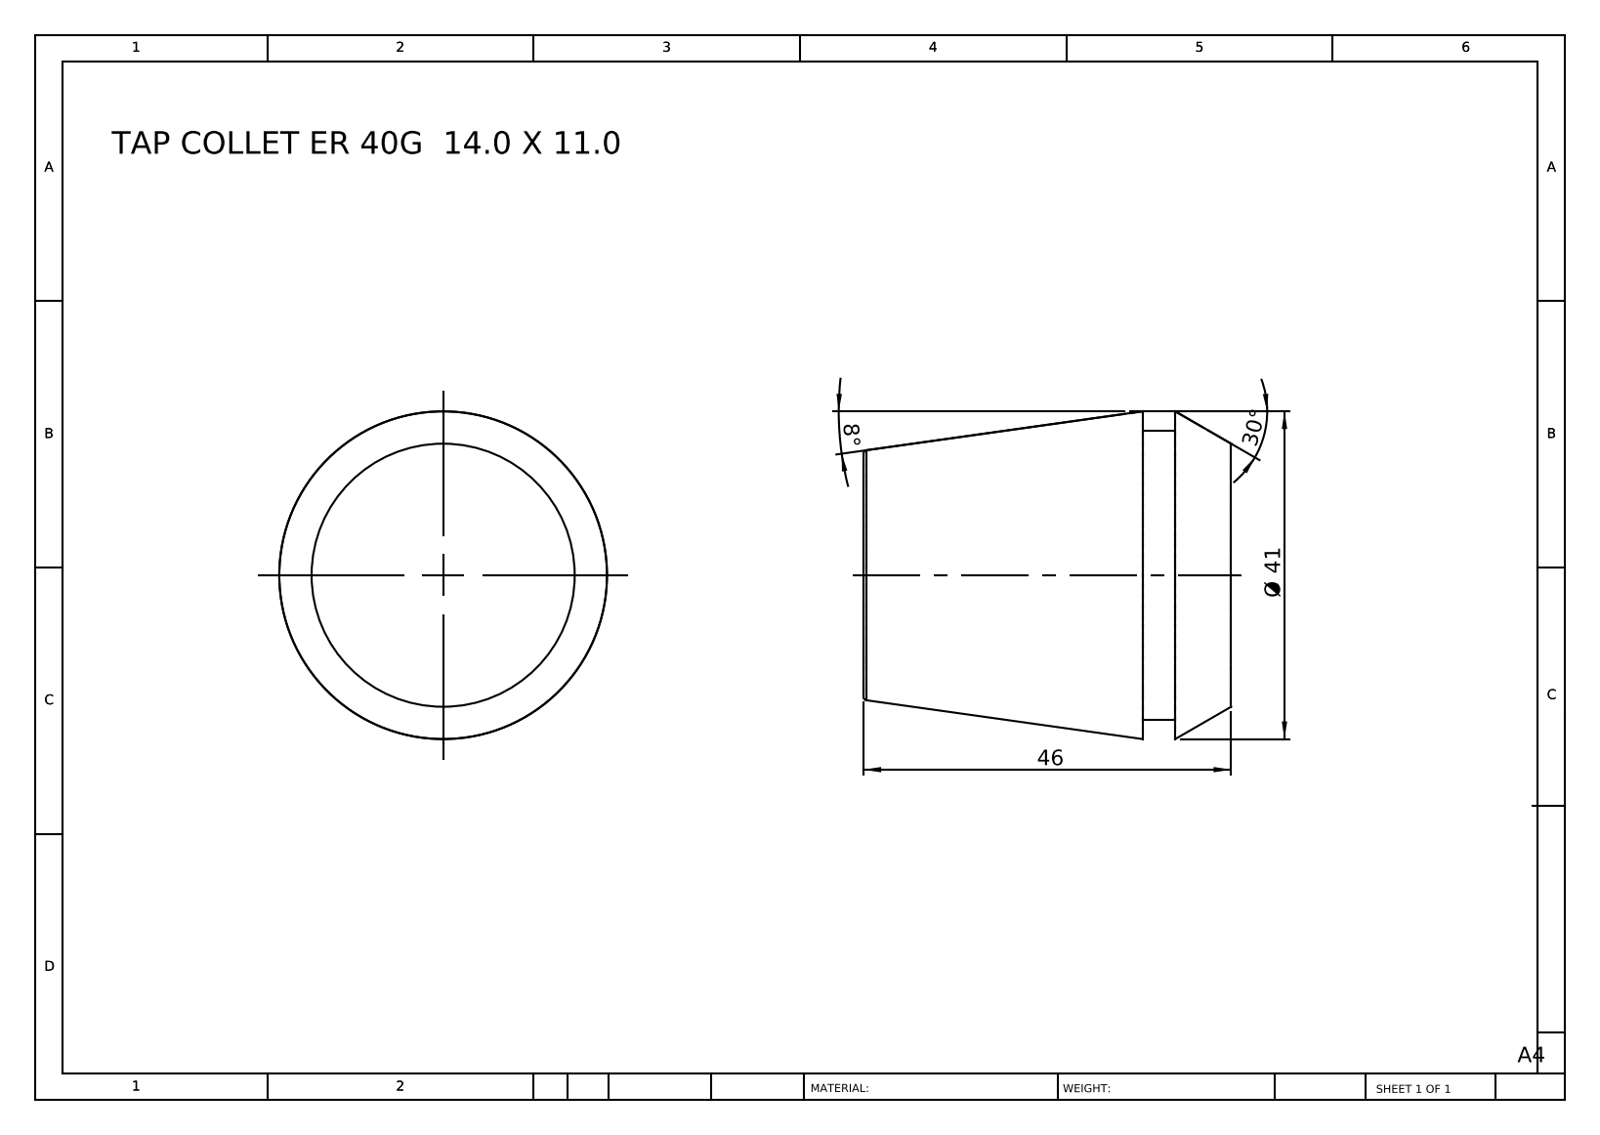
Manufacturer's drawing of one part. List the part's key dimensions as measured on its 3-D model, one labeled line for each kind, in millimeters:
Part name (STEP PRODUCT): TAP COLLET ER 40G 14.0 X 11.2
STEP written by: SolidWorks 2014 (CONFIG_CONTROL_DESIGN)
Units: millimetres
Bodies: 1 solid, 12 faces (4 planar, 2 cylindrical, 6 other)
Overall size (bounding box): 46 × 41 × 41
Volume: 47 690 mm³ · Surface area: 7 586 mm²
Round bosses / shafts (diameter × count): ⌀36.2 ×1
Main face-to-face distances: 46, 11.1, 34.9, 7, 4.1, 39
